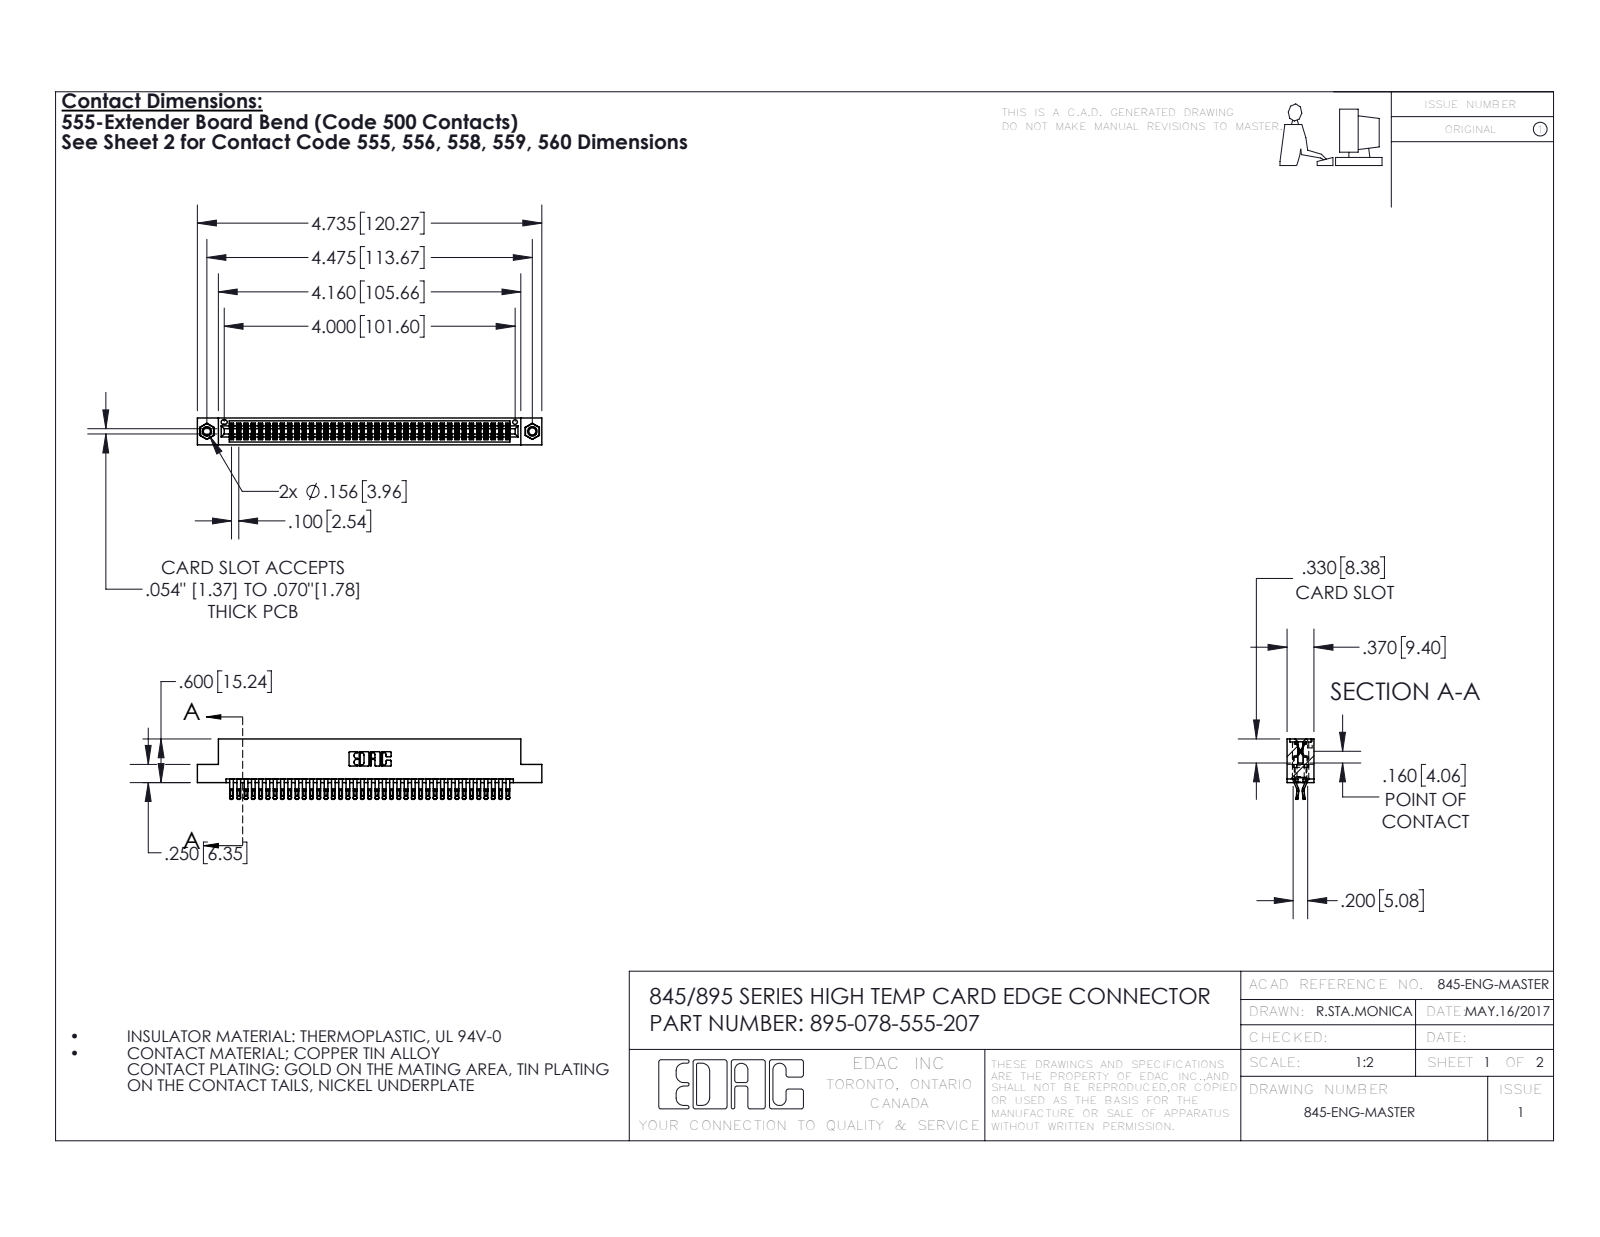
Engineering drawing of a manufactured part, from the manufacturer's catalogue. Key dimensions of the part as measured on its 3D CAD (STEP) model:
Part name (STEP PRODUCT): 345-250-001_345-250-005-103; 345 Part_Flush Mounting Lugs - 0.156 Dia-TI; 395-078-555-207; 345-292-001_555 Tail
STEP written by: SolidWorks 2016 (CONFIG_CONTROL_DESIGN)
Units: inches
Bodies: 81 solids, 4554 faces (2530 planar, 2008 cylindrical, 16 other)
Overall size (bounding box): 4.735 × 0.832 × 0.37
Volume: 0.724 in³ · Surface area: 28.36 in²
Round holes (diameter × count): ⌀0.098 ×2, ⌀0.125 ×2, ⌀0.156 ×2, ⌀0.064 ×1
Round bosses / shafts (diameter × count): ⌀0.155 ×2
Partial cylindrical surfaces — rounded edges, fillets, slot ends (radius × count): R0.016 ×195, R0.02 ×156, R0.006 ×117, R0.01 ×22, R0.007 ×6, R0.031 ×6, R0.026 ×3, R0.01 ×2
Main face-to-face distances: 0.072, 0.298, 0.025, 0.37, 0.2, 0.098, 0.272, 0.225, 0.175, 0.149
Hole centre spacings: 0.27, 4.239, 4.475
